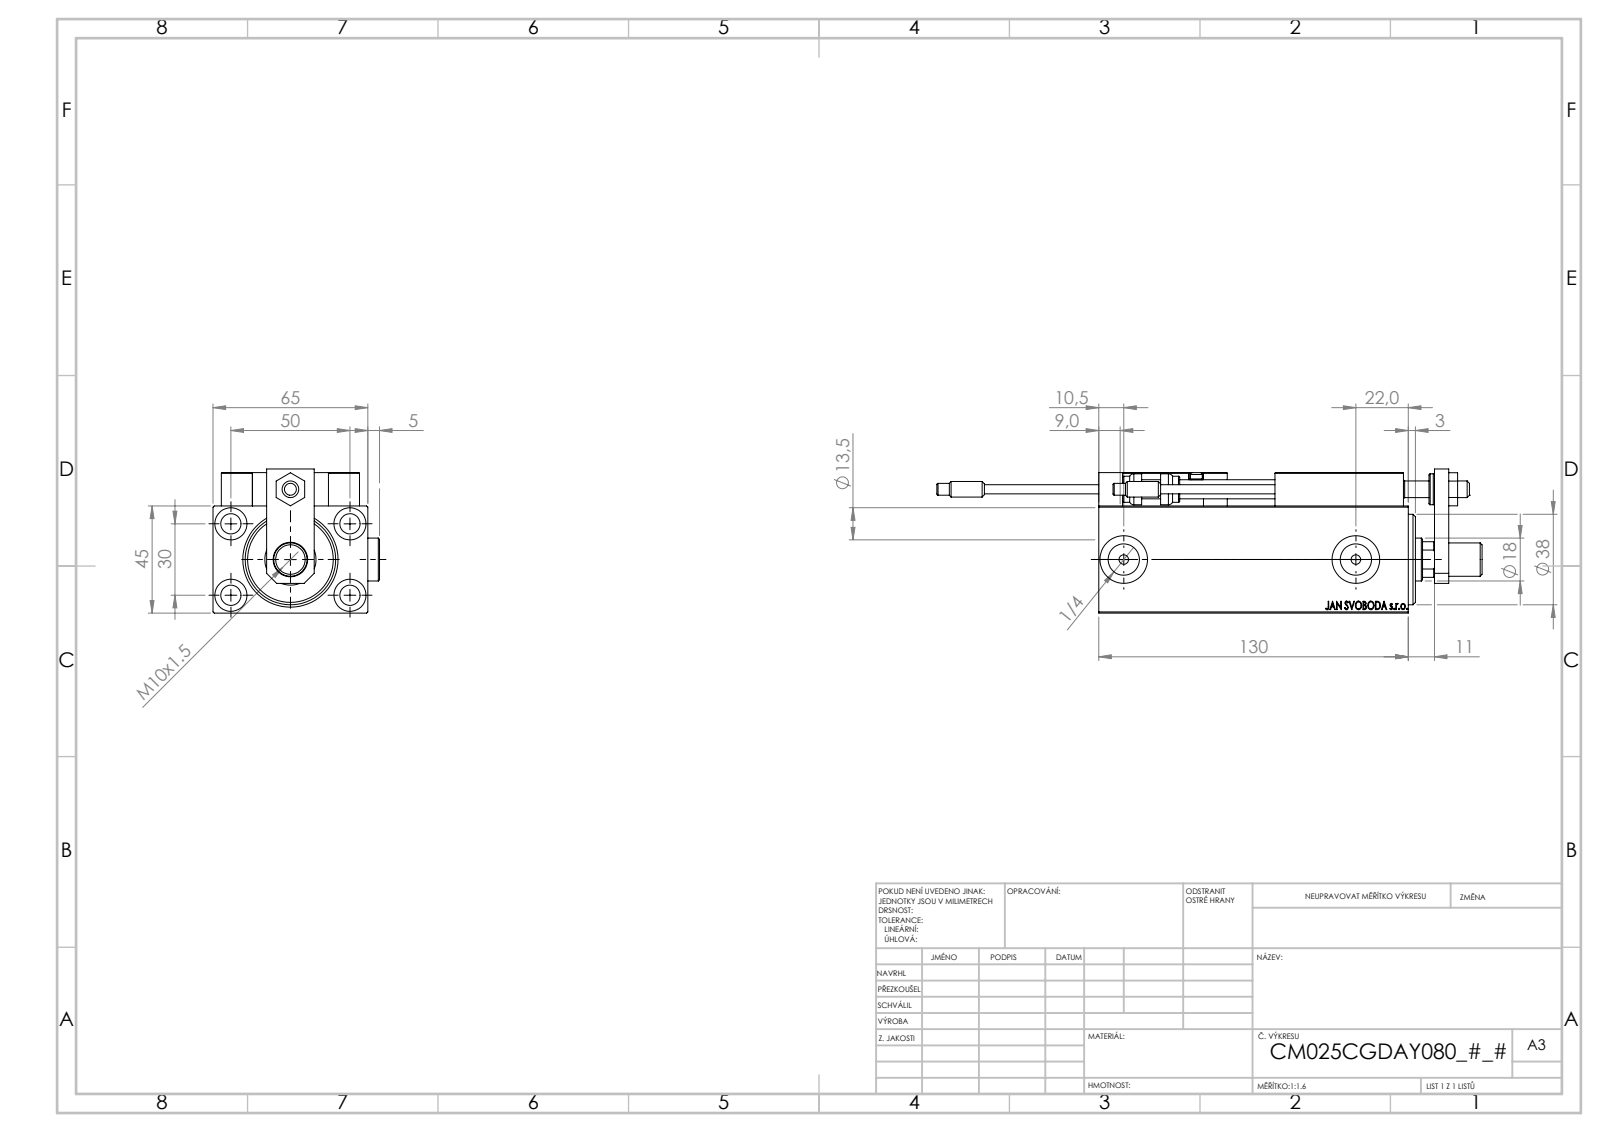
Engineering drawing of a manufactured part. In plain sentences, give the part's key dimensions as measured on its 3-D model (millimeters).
The part is named "MAGNET; Zatka_OIL_PORT; SWITCH_X_FRONT_BACK; V450CM_C_VCP (+7 more)". Its 3-D file was written by "SolidWorks 2019 (CONFIG_CONTROL_DESIGN)". It is 26 solids with 1371 faces: 599 planar, 216 cylindrical and 556 other. Overall it measures 229 by 69.9 by 60.5 millimeters. Its volume is 376 443 cubic millimeters and its surface area 103 199 square millimeters. Round holes: 6 of diameter 4, 5 of diameter 8, 5 of diameter 8.5, 4 of diameter 3.2, 4 of diameter 13.5, 2 of diameter 5, 2 of diameter 13.16, 2 of diameter 20, 1 of diameter 7, 1 of diameter 14.5, 1 of diameter 18, 1 of diameter 21.5. Round bosses or shafts: 4 of diameter 5, 2 of diameter 18, 2 of diameter 6.5, 2 of diameter 3.8, 1 of diameter 14, 1 of diameter 13, 1 of diameter 12, 1 of diameter 11. Partial cylindrical surfaces (rounded edges, fillets, slot ends): 30 of radius 0.3, 2 of radius 3, 1 of radius 8.5. The main face-to-face distances are 45, 65, 14, 6, 59, 3, 5, 13, 3.5, 20. The hole center spacings are 29.15, 11.37, 20, 28.9, 29.59, 29.69, 30, 36.06.
